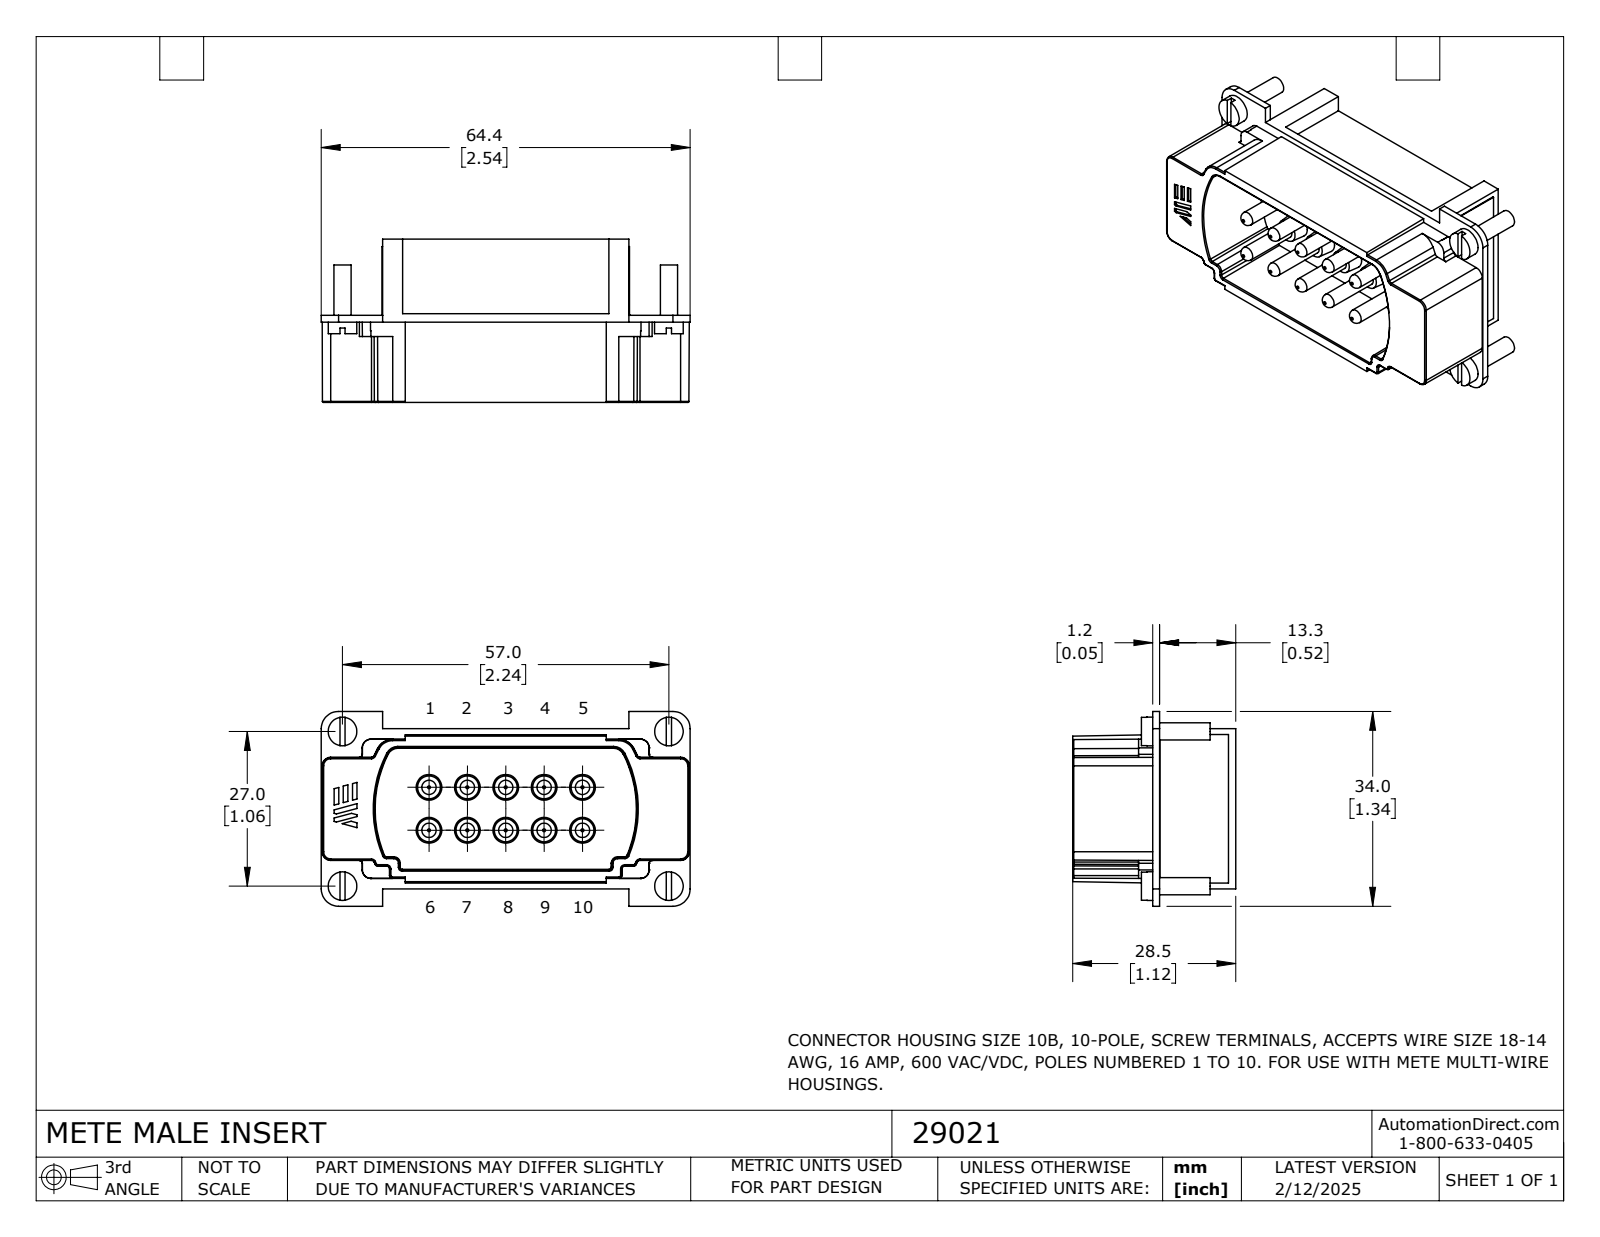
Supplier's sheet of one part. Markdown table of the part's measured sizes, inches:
| quantity | value |
| --- | --- |
| part name | 29021 |
| STEP written by | SolidWorks 2024 (CONFIG_CONTROL_DESIGN) |
| units | inches |
| bodies | 1 solid, 330 faces (161 planar, 60 cylindrical, 109 other) |
| overall size | 2.536 × 1.339 × 1.122 |
| volume | 1.501 in³ |
| surface area | 18.42 in² |
| round bosses / shafts (diameter × count) | 0.098 × 10, 0.197 × 4, 0.118 × 4 |
| partial cylindrical surfaces (radius × count) | 0.008 × 14, 0.118 × 4 |
| main face-to-face distances | 0.571, 0.524, 0.047, 0.598, 0.866, 1.122, 0.551, 0.118, 1.702, 0.984 |
